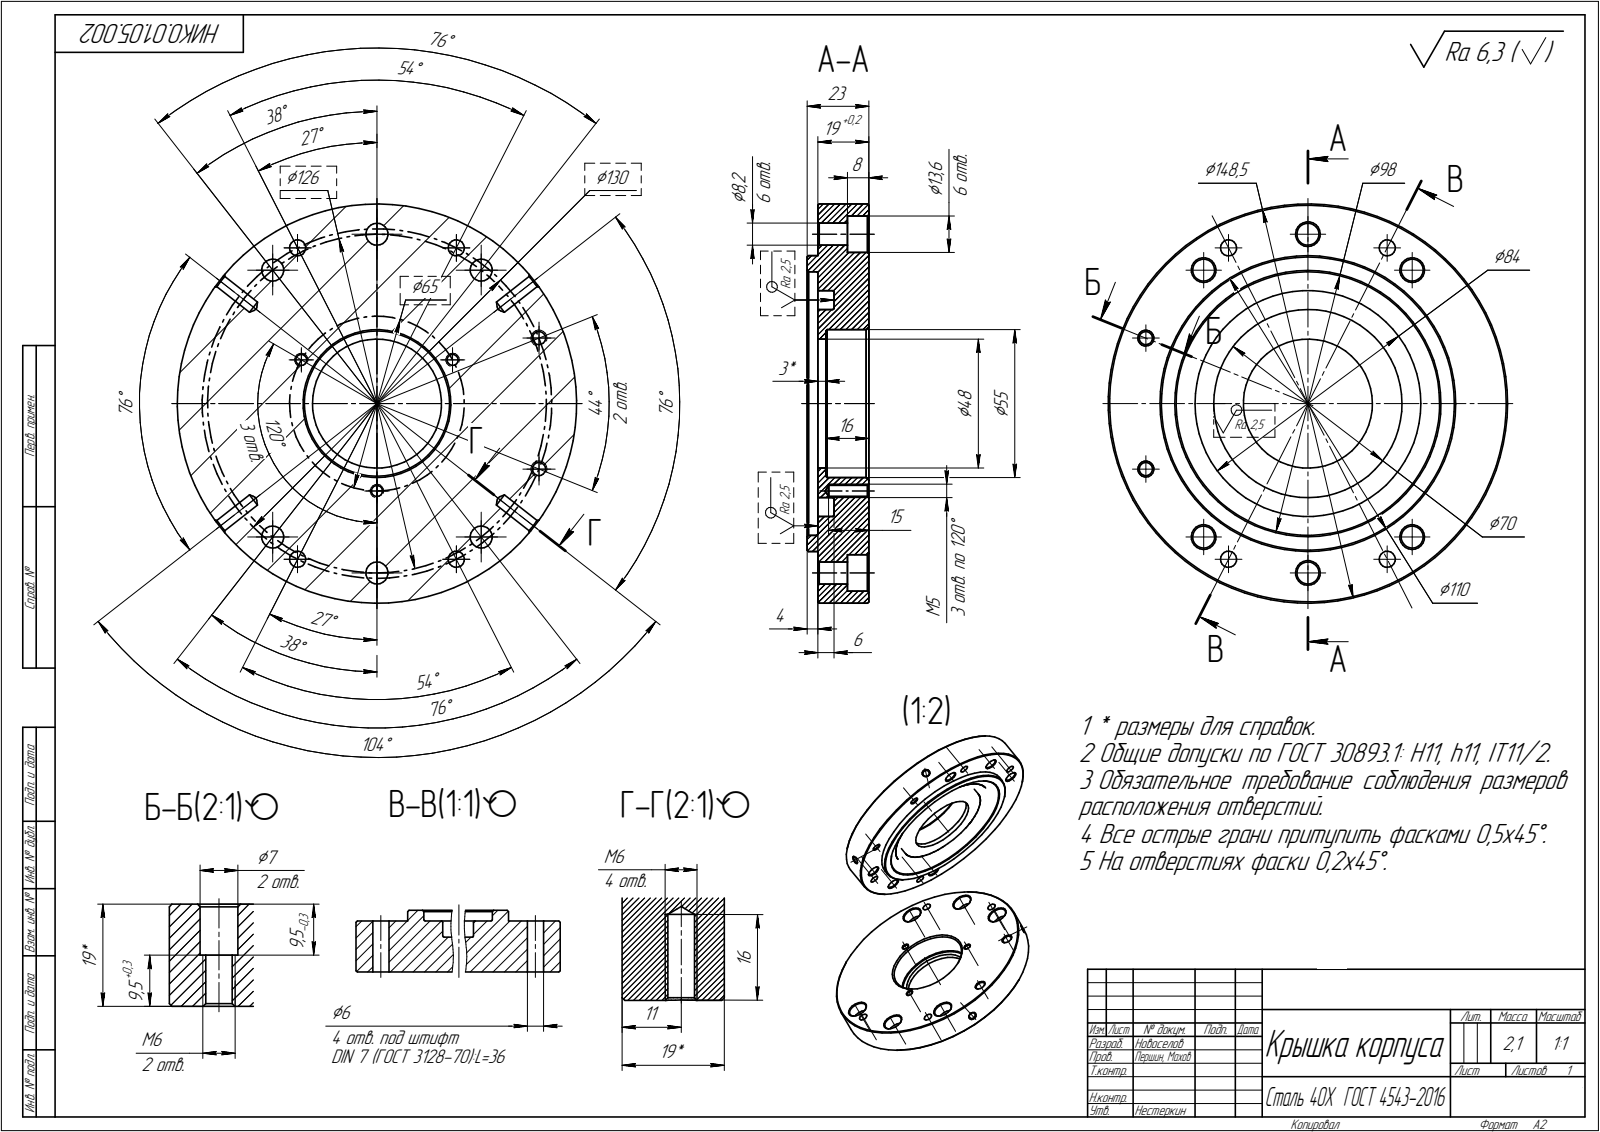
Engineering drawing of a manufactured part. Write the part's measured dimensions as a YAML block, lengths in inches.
part_name: "Крышка корпуса"
step_written_by: "SolidWorks 2020 (AUTOMOTIVE_DESIGN)"
units: inches
bodies: {solids: 1, faces: 119, planar: 49, cylindrical: 50, other: 20}
overall_size: [10.827, 6.89, 0.197]
volume: 9.129
surface_area: 117.3
round_holes:
  - {diameter: 0.157, count: 6}
  - {diameter: 0.079, count: 2}
partial_cylinders:
  - {radius: 0.197, count: 10}
  - {radius: 0.079, count: 8}
  - {radius: 0.177, count: 6}
  - {radius: 0.02, count: 4}
  - {radius: 0.098, count: 4}
  - {radius: 0.059, count: 2}
face_to_face_distances: [0.197, 0.039, 0.079, 0.157, 0.118, 0.059, 0.02, 0.138, 0.098, 1.713]
hole_center_spacings: [6.457, 0.602, 5.201, 6.306, 8.291, 9.828, 10.402, 11.662]
